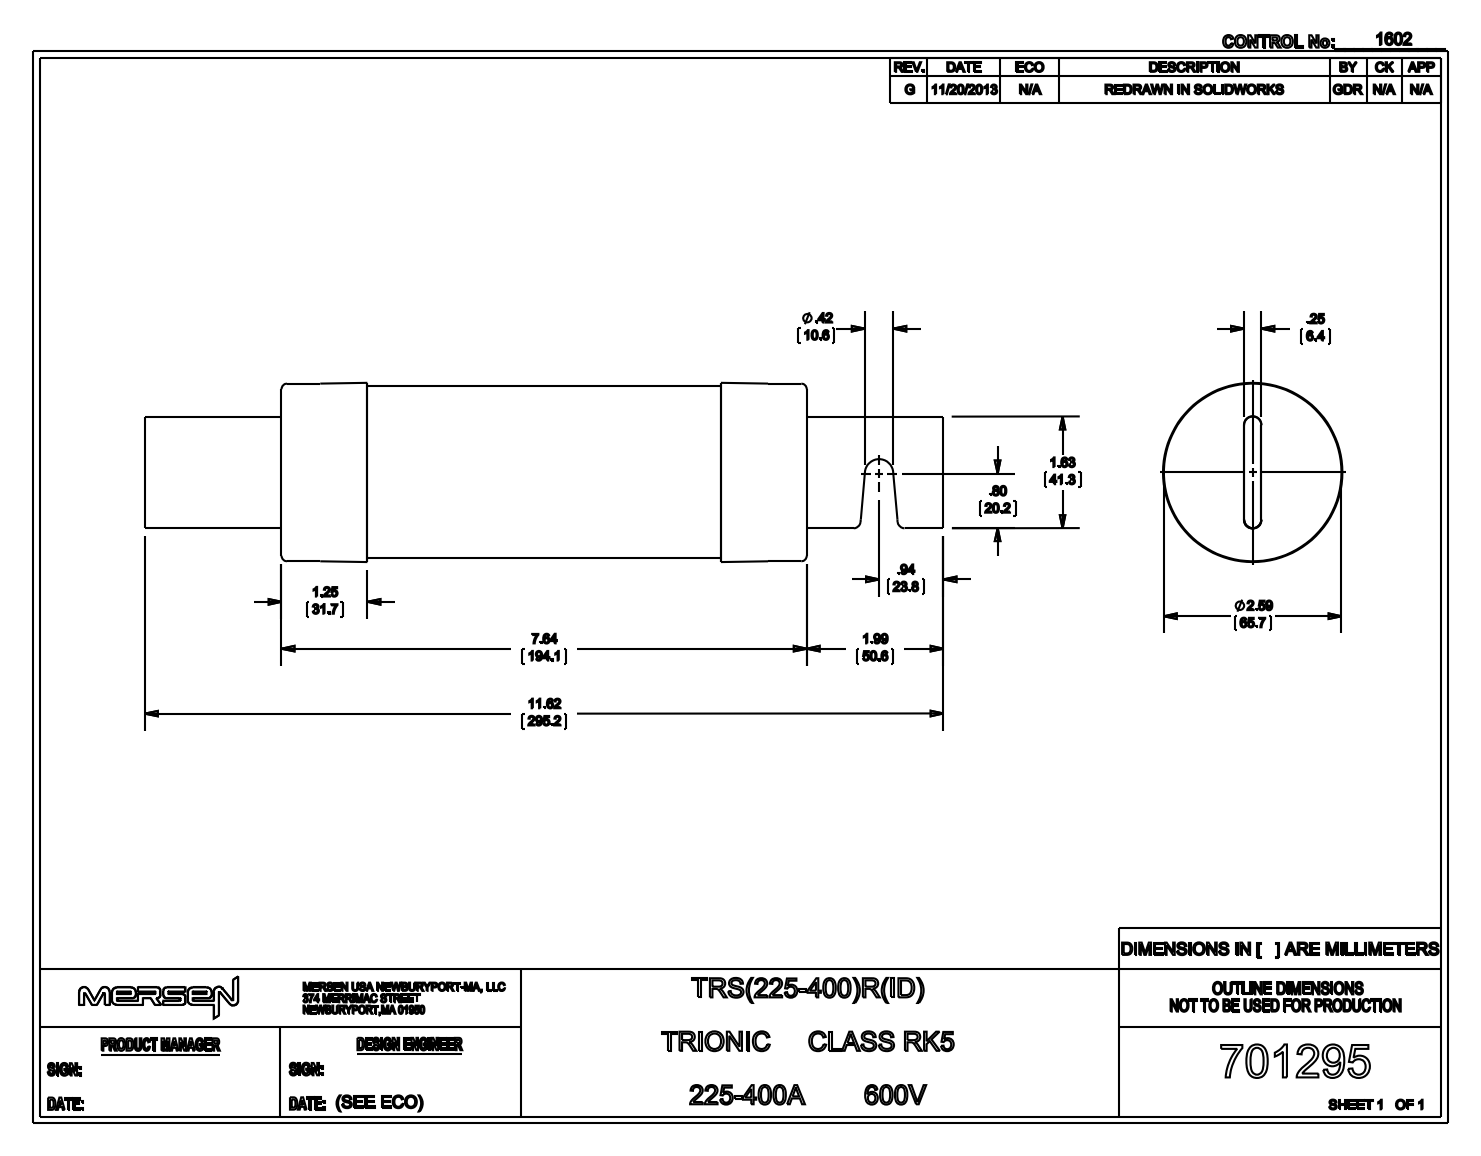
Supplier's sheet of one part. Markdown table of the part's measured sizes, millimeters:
| quantity | value |
| --- | --- |
| part name | 701295revA |
| STEP written by | SolidWorks 2013 (AUTOMOTIVE_DESIGN) |
| units | millimeters |
| bodies | 7 solids, 86 faces (36 planar, 36 cylindrical, 14 other) |
| overall size | 295.2 × 66.3 × 66.3 |
| volume | 191 200 mm³ |
| surface area | 139 900 mm² |
| round holes (diameter × count) | 6.4 × 2, 6.5 × 2, 57.2 × 1, 63.6 × 1 |
| round bosses / shafts (diameter × count) | 65.7 × 1, 65.7 × 1, 63.5 × 1, 61.6 × 1 |
| partial cylindrical surfaces (radius × count) | 3.2 × 4, 2.5 × 2, 3 × 2, 3.3 × 2, 5.6 × 2, 3.2 × 1, 5.3 × 1 |
| main face-to-face distances | 6.4, 3.2, 188.9, 1, 4.2, 189.9, 193.1, 192.1, 185.7, 194.1 |
| hole center spacings | 155.5 |
